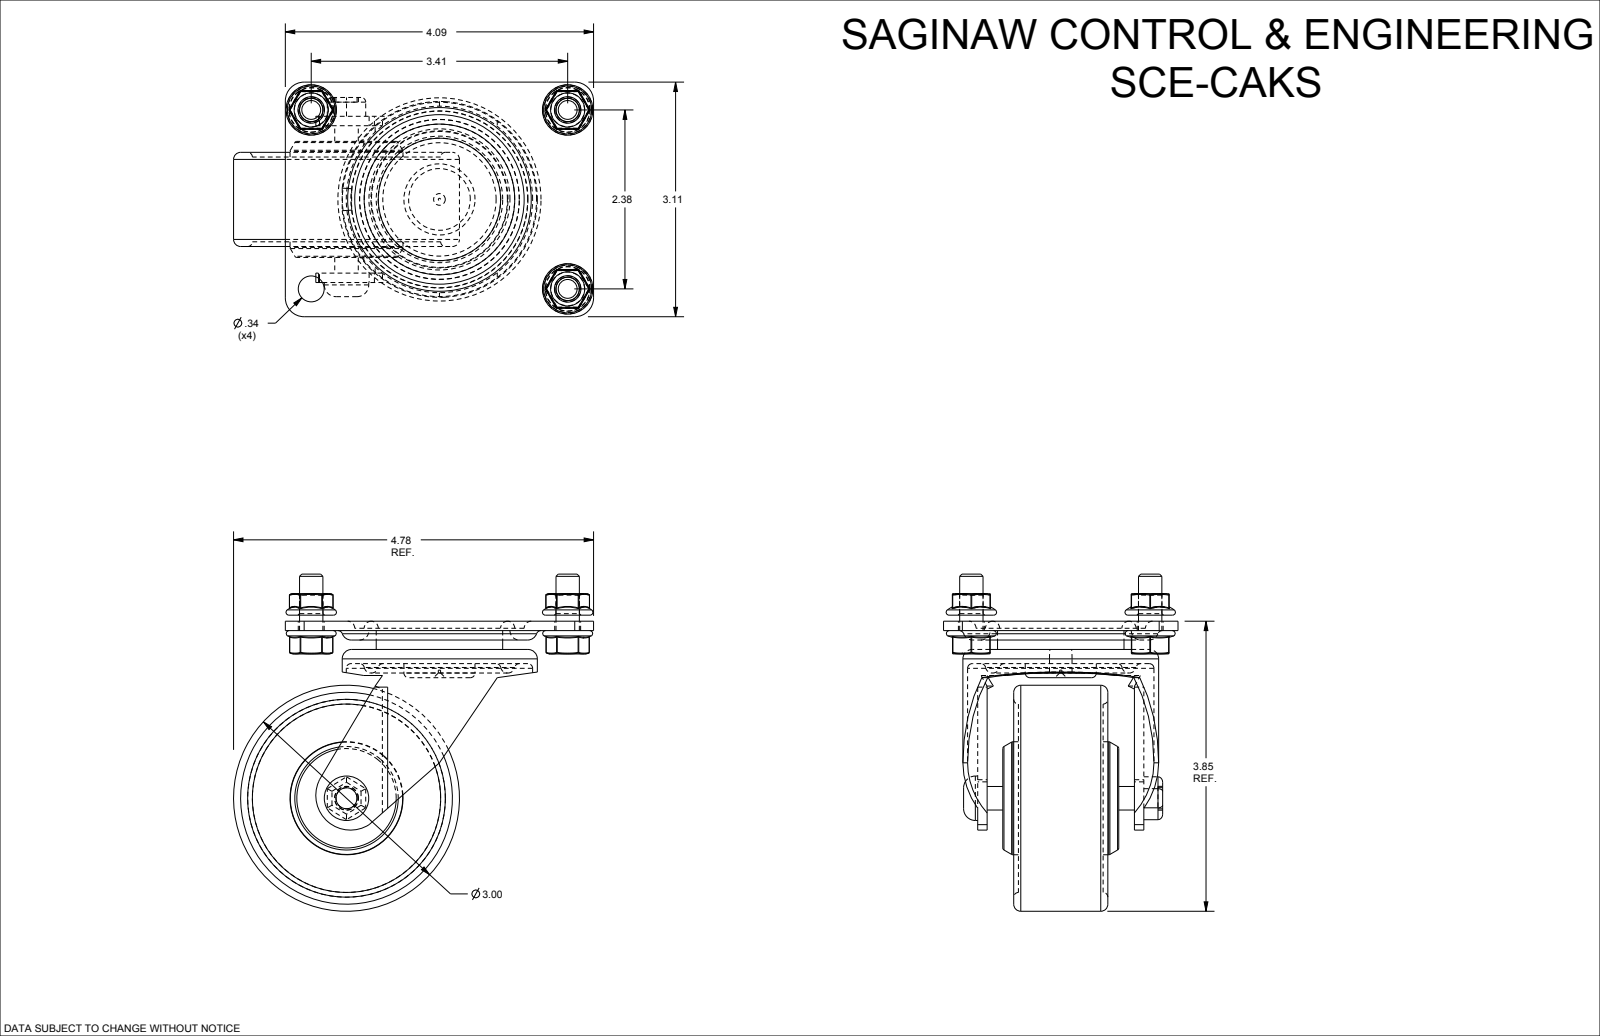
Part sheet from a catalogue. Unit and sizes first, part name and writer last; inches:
Units: inches
Overall size (bounding box): 30.688 × 30 × 4.475
Round holes (diameter × count): ⌀0.312 ×16, ⌀0.344 ×16, ⌀0.03 ×4, ⌀0.316 ×2, ⌀2.475 ×2, ⌀2.475 ×2
Round bosses / shafts (diameter × count): ⌀0.31 ×16, ⌀2.6 ×4, ⌀1.68 ×4, ⌀0.944 ×4, ⌀3 ×2, ⌀1.5 ×2, ⌀0.59 ×2, ⌀0.313 ×2
Partial cylindrical surfaces — rounded edges, fillets, slot ends (radius × count): R0.01 ×192, R0.062 ×24, R0.25 ×16, R0.125 ×2, R0.46 ×2
Main face-to-face distances: 0.125, 26.886, 1.125, 0.25, 0.031, 0.094, 0.207, 1.333, 0.125, 0.281
Hole centre spacings: 2.076, 26.886, 2.375, 24.232, 25.755, 27.101, 28.125, 25.906
Volume: 54.28 in³ · Surface area: 371.9 in²
Bodies: 36 solids, 1844 faces (492 planar, 344 cylindrical, 1008 other)
Part name (STEP PRODUCT): SCE-CAKS
STEP written by: SolidWorks 2019 (CONFIG_CONTROL_DESIGN)
